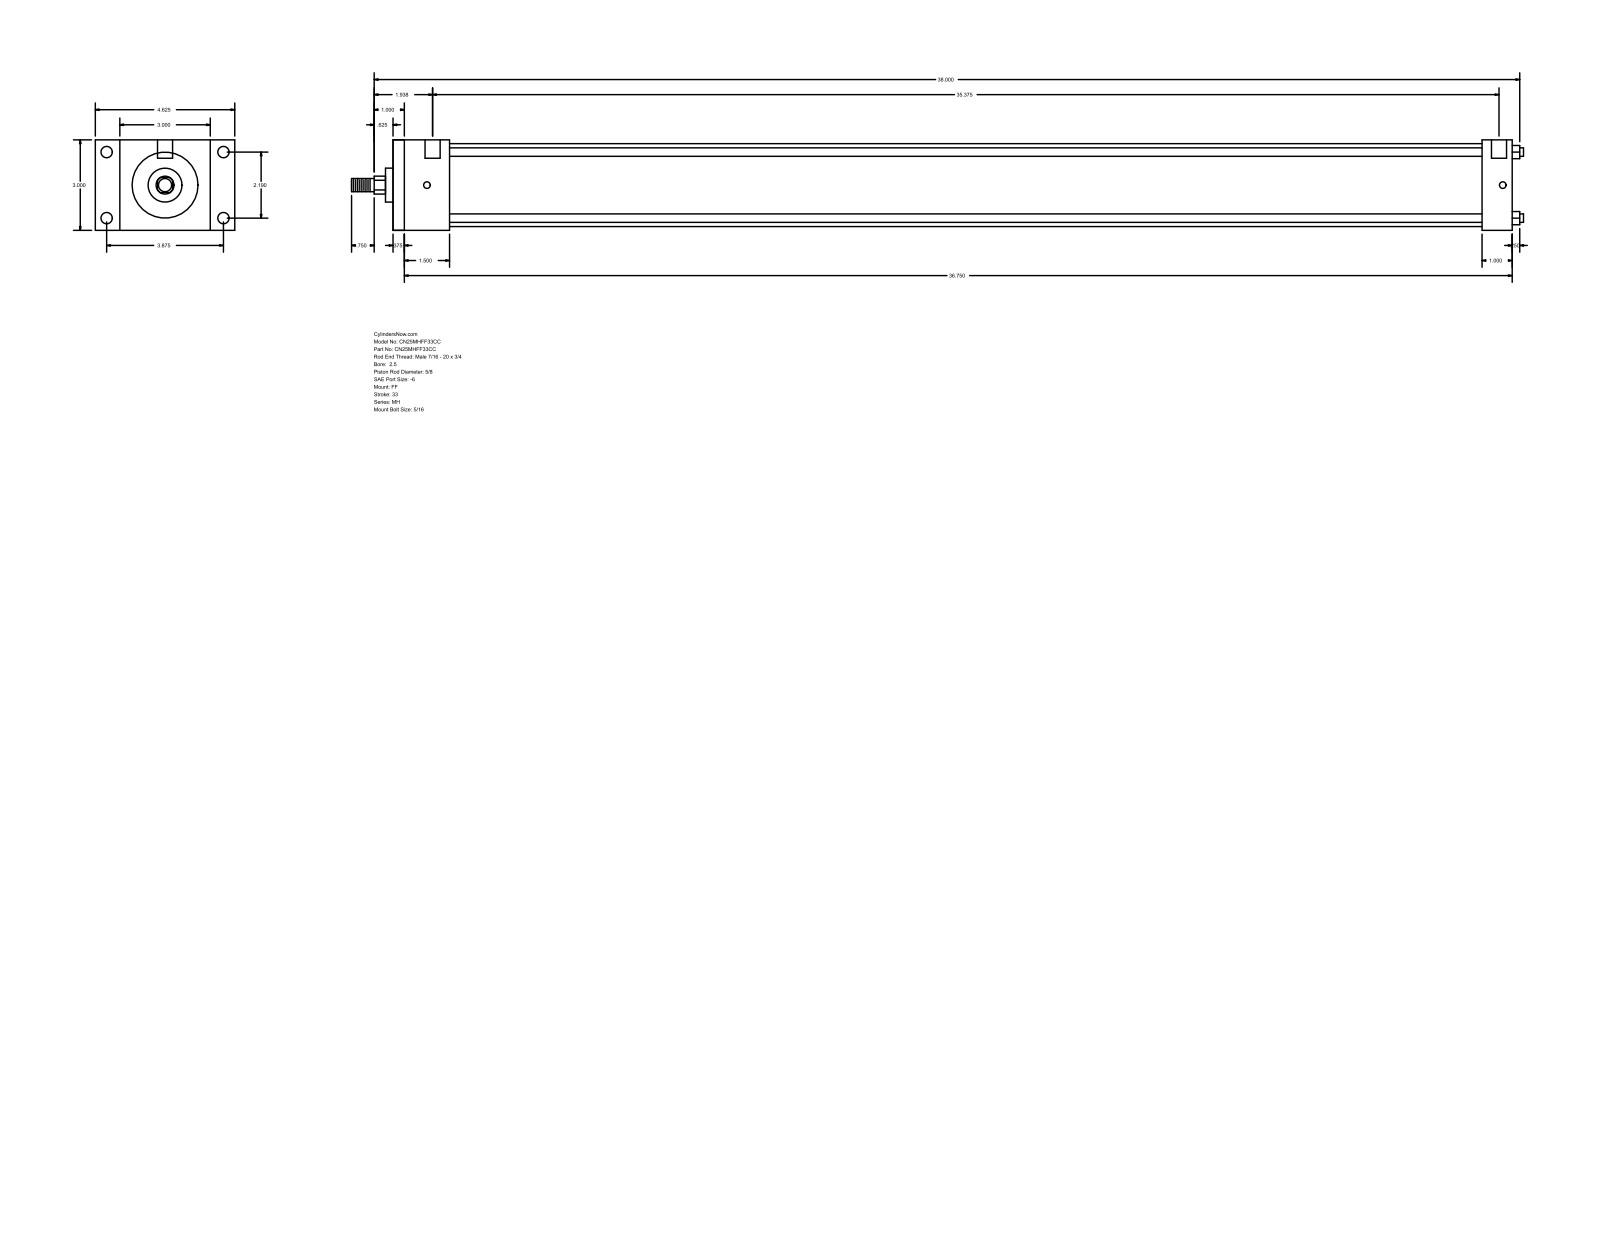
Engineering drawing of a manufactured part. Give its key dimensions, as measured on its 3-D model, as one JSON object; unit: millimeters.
{"part_name": "MH_FF__0250_0.625", "step_written_by": "GSSL Pune (CONFIG_CONTROL_DESIGN)", "units": "millimeters", "bodies": {"solids": 0, "faces": 92, "planar": 64, "cylindrical": 28, "other": 0}, "overall_size": [987.42, 117.47, 76.2], "round_holes": [[5.56, 4], [9.53, 4], [12.7, 2]], "round_bosses_or_shafts": [[7.14, 4], [69.85, 1], [28.57, 1], [15.88, 1], [11.11, 1]], "partial_cylinders_radius": [[7.54, 1]], "face_to_face_distances": [76.2, 942.97, 933.45, 9.52, 25.4, 47.62, 917.57, 38.1, 908.05, 869.95], "hole_center_spacings": [55.62, 98.42, 113.05, 906.46, 3.17, 4.76, 898.53, 901.7]}
